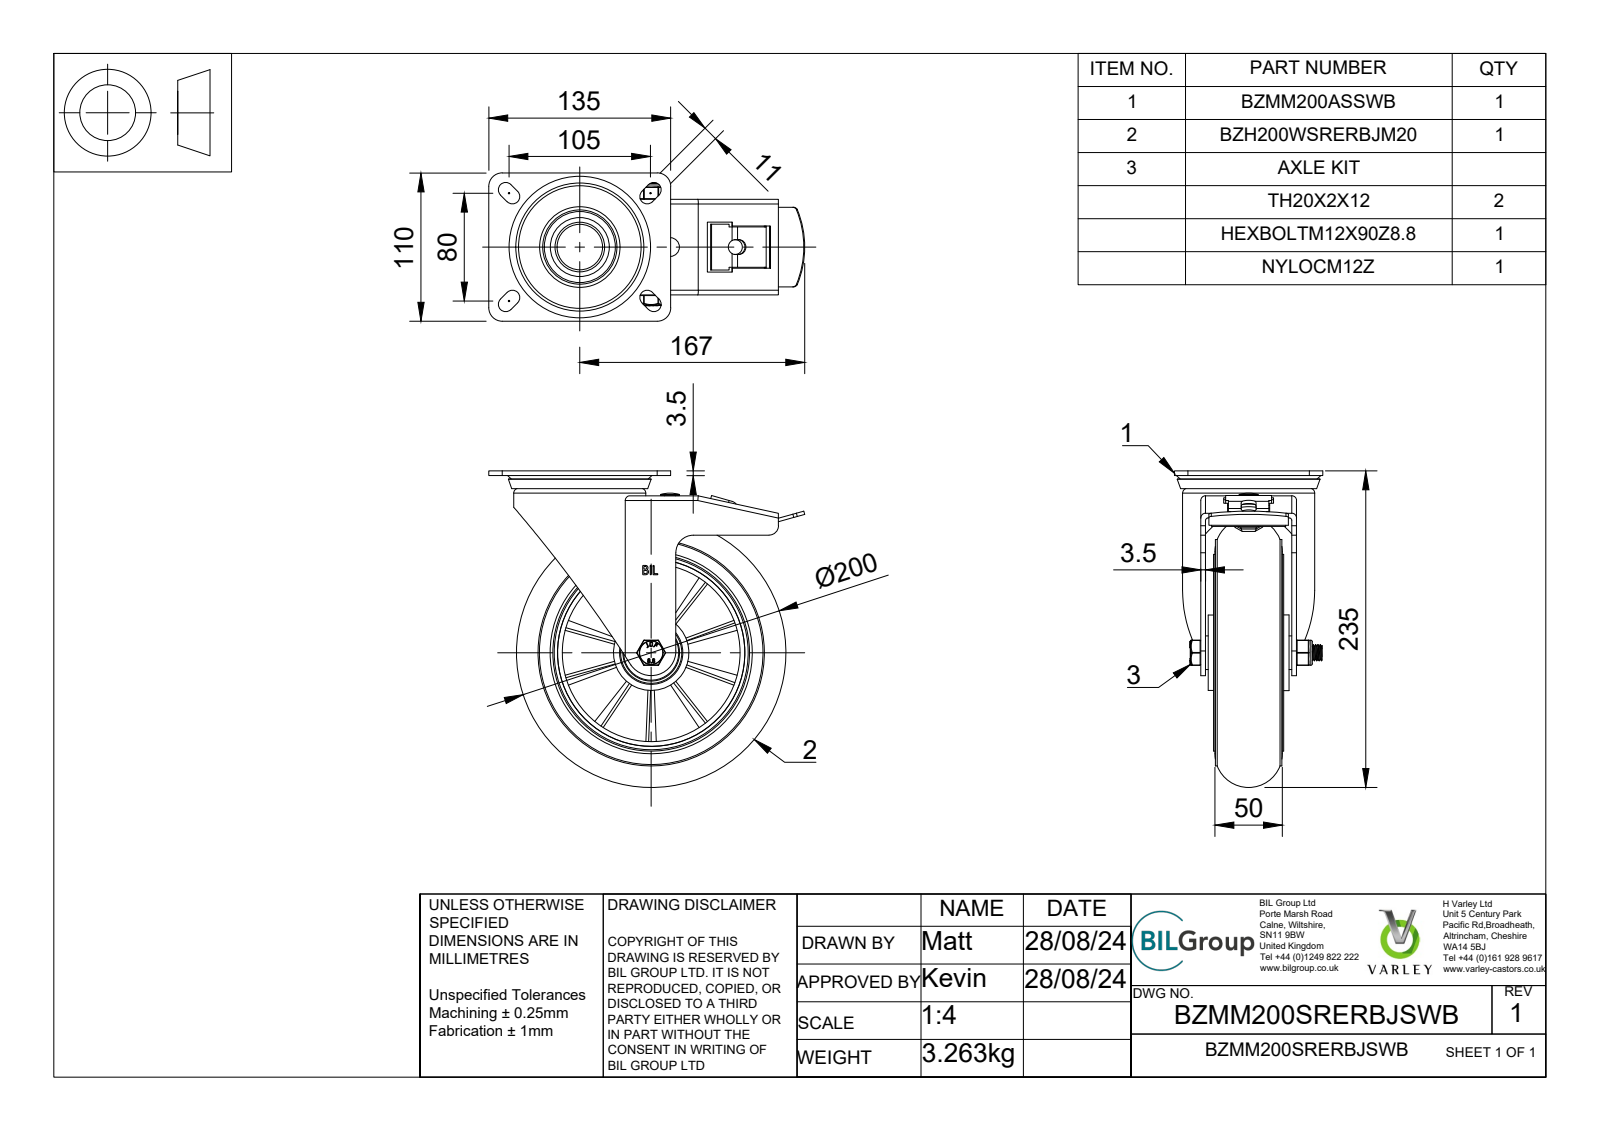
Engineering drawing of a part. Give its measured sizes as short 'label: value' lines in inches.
name: BZMM200SRERBJSWB v3; BZMM200ASSWB - 64 v1; ZINC PLATED, PRESSED STEEL TOP PLATE; ZINC PLATED, PRESSED STEEL TOP PLATE Geometry (+7 more)
written by: Autodesk Translation Framework v13.14.0.145 (AUTOMOTIVE_DESIGN)
unit: in
bodies: 82 solids, 1341 faces (573 planar, 256 cylindrical, 512 other)
size: 9.252 × 9.232 × 4.331
volume: 67.49 in³; area: 591.1 in²
holes: 1× ⌀0.315, 1× ⌀0.433, 1× ⌀0.472, 1× ⌀0.48, 1× ⌀0.551, 1× ⌀0.787, 1× ⌀1.122, 1× ⌀1.213, 1× ⌀1.329, 1× ⌀1.587, 1× ⌀1.594, 1× ⌀1.654
bosses: 1× ⌀6.614, 1× ⌀5.748, 1× ⌀3.858, 1× ⌀3.071, 1× ⌀2.213, 1× ⌀2.205, 1× ⌀1.969, 1× ⌀1.606
rounds: 19× R0.02, 10× R0.217, 7× R0.069, 6× R0.01, 6× R0.098, 4× R0.019, 4× R0.035, 4× R0.138
face distances: 0.138, 0.079, 0.354, 0.217, 0.512, 2.657, 1.88, 0.561, 0.157, 0.374
hole spacings: 2.638
